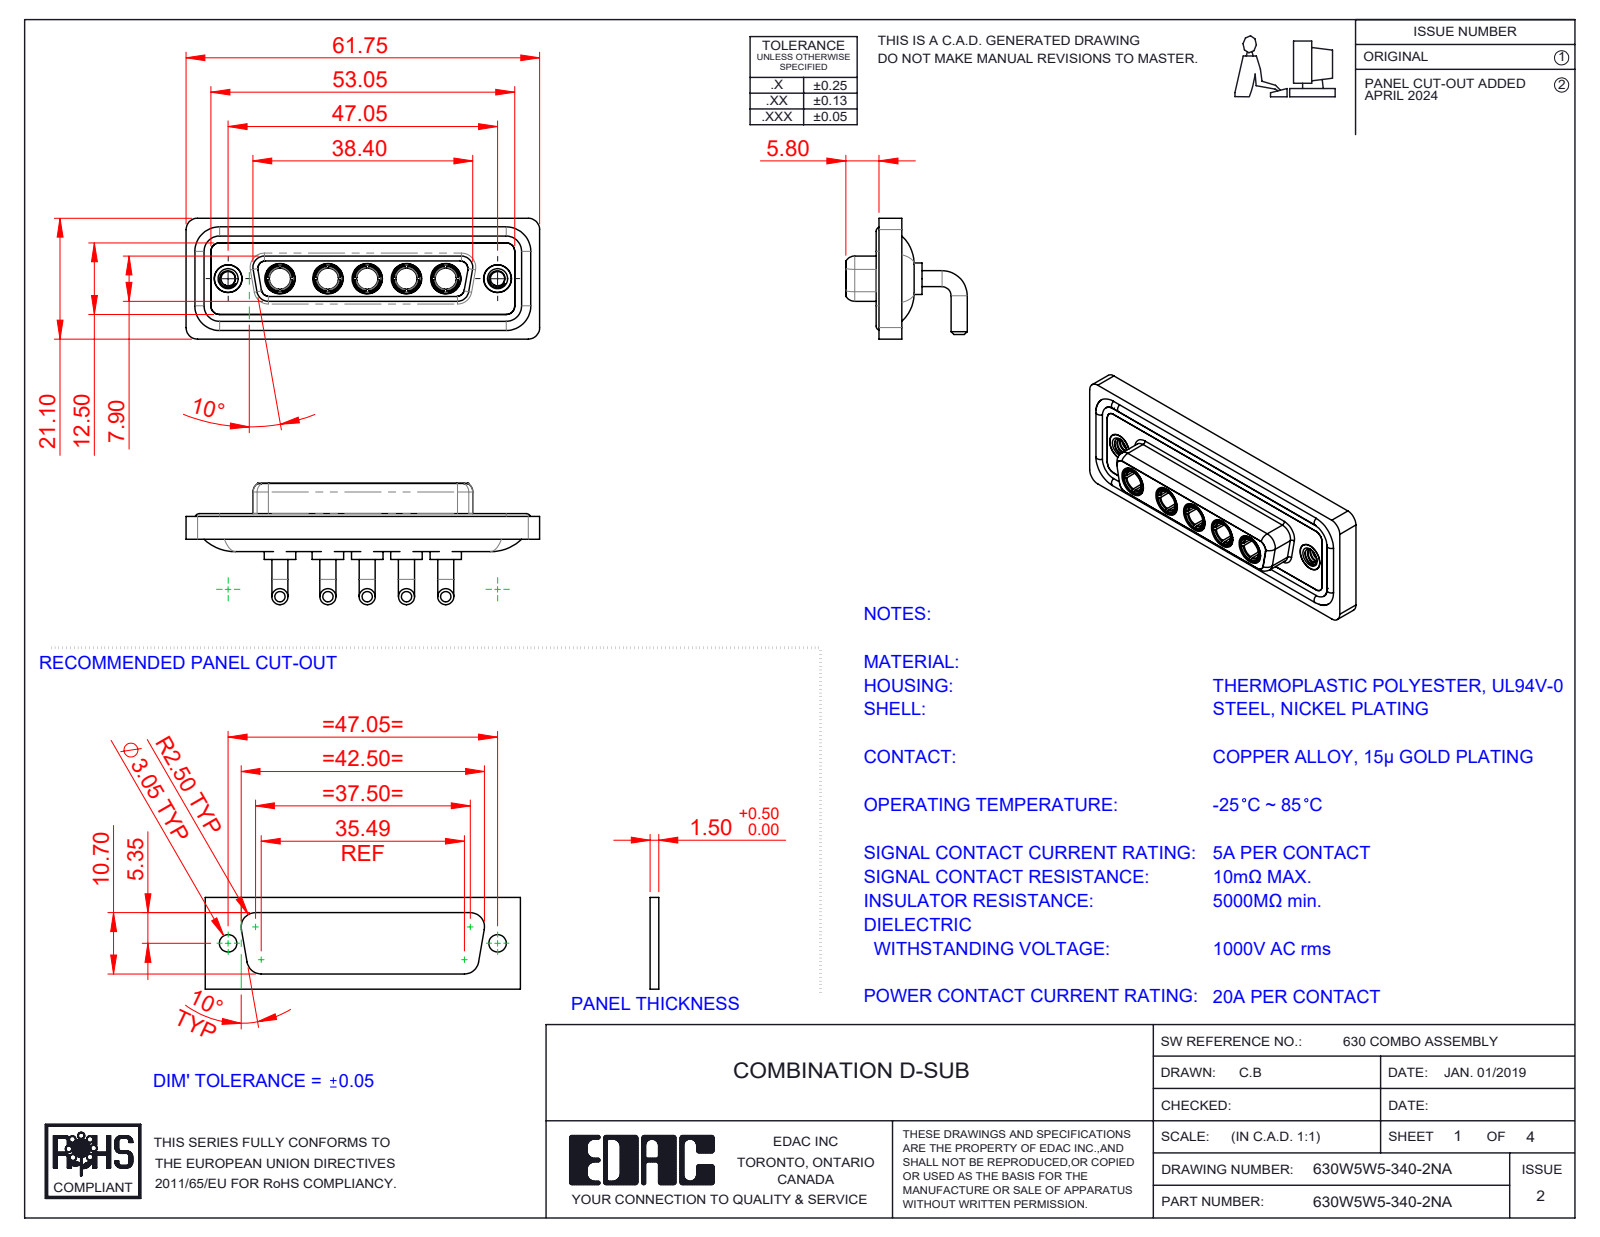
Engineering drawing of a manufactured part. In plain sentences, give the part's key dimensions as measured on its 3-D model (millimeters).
The part is named "630Combo Waterproof Housing_25 Contacts; Power Socket_20A RA; 630Combo Shell Front_25 Contacts; 630Combo Housing_5W5 (+3 more)". Its 3-D file was written by "SolidWorks 2023 (CONFIG_CONTROL_DESIGN)". It is 17 solids with 770 faces: 250 planar, 311 cylindrical and 209 other. Overall it measures 61.75 by 21.2 by 21.1 millimeters. Its volume is 8 428 cubic millimeters and its surface area 13 816 square millimeters. Round holes: 7 of diameter 4.85, 5 of diameter 3.7, 5 of diameter 5.3, 2 of diameter 2.5, 2 of diameter 4, 2 of diameter 4.05, 2 of diameter 5. Round bosses or shafts: 10 of diameter 2.8, 5 of diameter 5.5, 5 of diameter 5.2, 5 of diameter 4.96, 5 of diameter 4.75, 5 of diameter 3.75, 4 of diameter 1.6, 2 of diameter 4.95. Partial cylindrical surfaces (rounded edges, fillets, slot ends): 18 of radius 1.5, 18 of radius 2, 8 of radius 1.35, 8 of radius 1.6, 5 of radius 2.1, 4 of radius 0.25, 4 of radius 0.5, 4 of radius 0.6. The main face-to-face distances are 0.4, 1.8, 4.1, 1.1, 1.5, 2.5, 3.1, 3.7, 1.6, 2.9. The hole center spacings are 6.86, 9.04, 38.01, 6.87, 8.38, 13.72, 13.73, 15.25.
